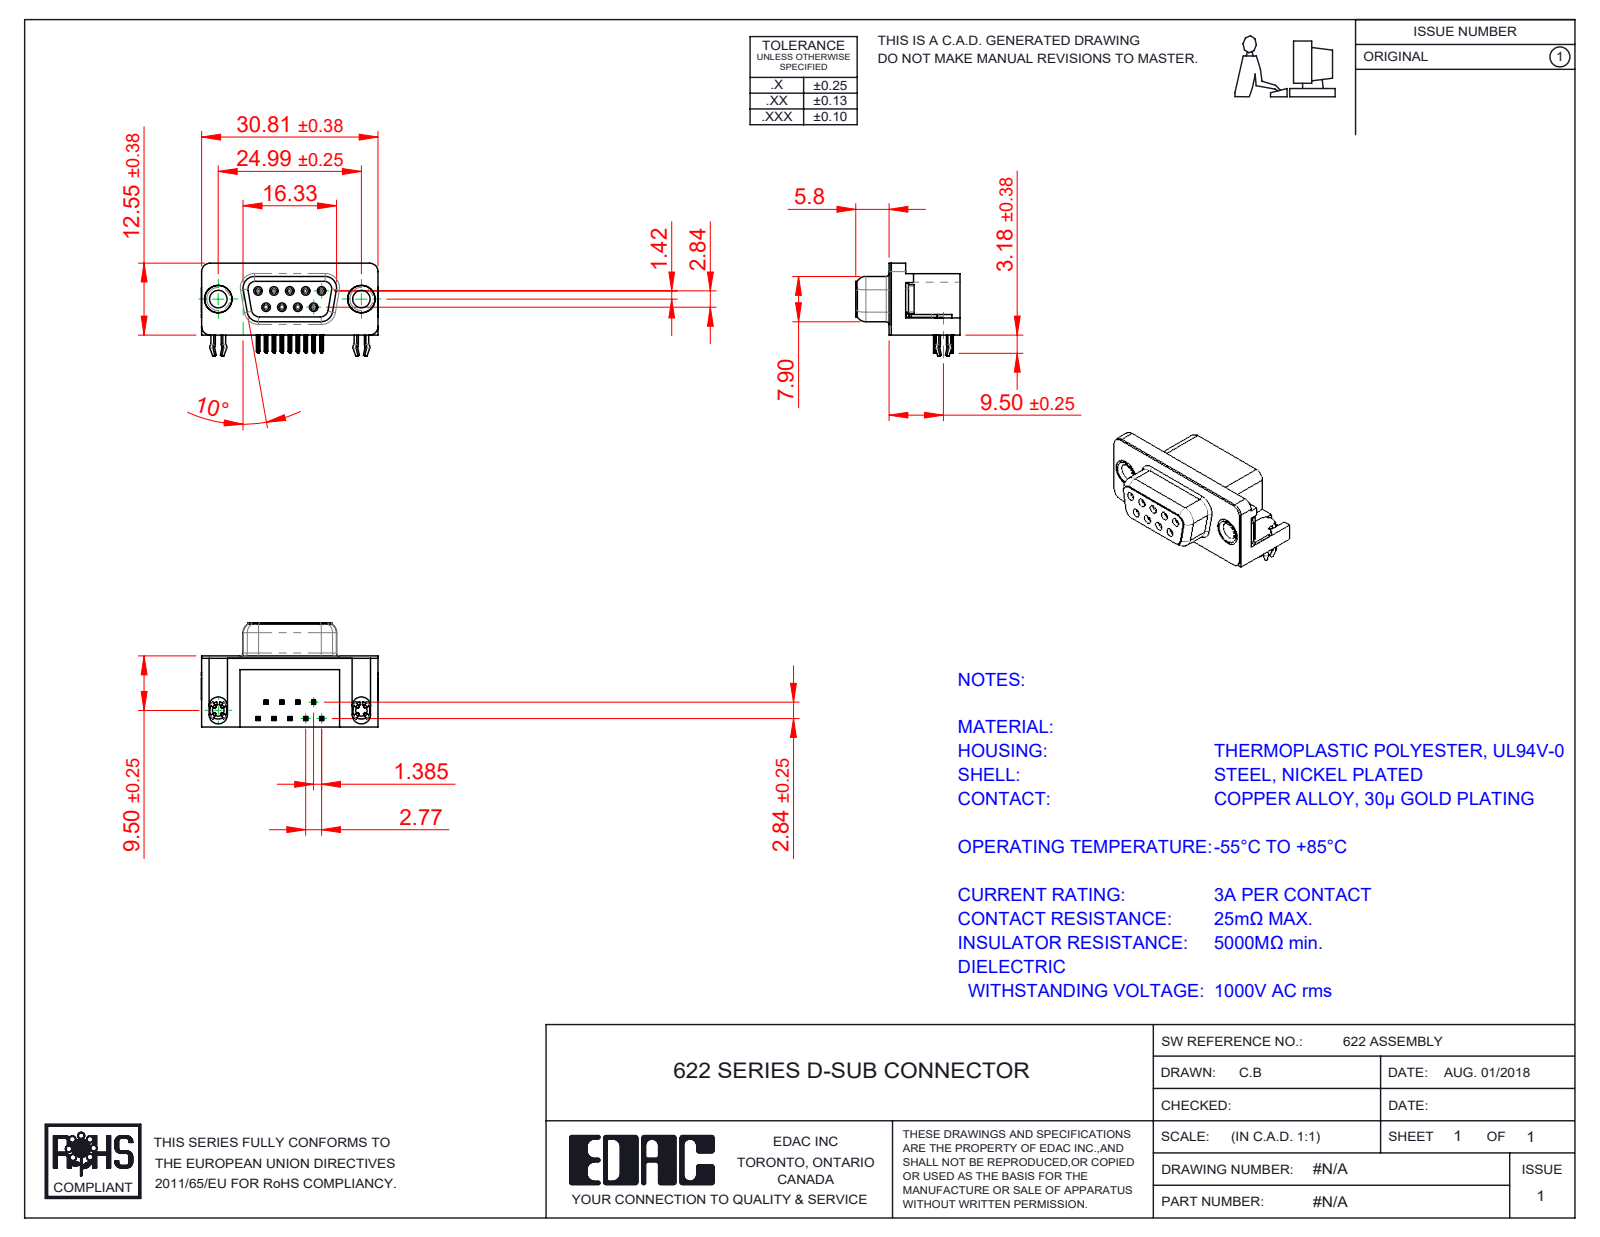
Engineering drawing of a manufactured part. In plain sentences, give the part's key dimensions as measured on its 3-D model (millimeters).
The part is named "622-009-668-051; 622 Thru Hole Rivet; 622 Socket Bottom; 622 Contact Top (+3 more)". Its 3-D file was written by "SolidWorks 2016 (CONFIG_CONTROL_DESIGN)". It is 15 solids with 1562 faces: 684 planar, 410 cylindrical and 468 other. Overall it measures 30.89 by 18.2 by 15.73 millimeters. Its volume is 3 725 cubic millimeters and its surface area 5 129 square millimeters. Round holes: 9 of diameter 0.8, 9 of diameter 0.9, 2 of diameter 2.26, 2 of diameter 3.05, 2 of diameter 4, 2 of diameter 4.8, 2 of diameter 5. Round bosses or shafts: 9 of diameter 1.2, 2 of diameter 4.9, 2 of diameter 4.75, 2 of diameter 3.85, 2 of diameter 3.26. Partial cylindrical surfaces (rounded edges, fillets, slot ends): 72 of radius 0.1, 36 of radius 0.15, 18 of radius 0.35, 18 of radius 1, 9 of radius 0.34, 8 of radius 0.25, 8 of radius 1.35, 8 of radius 1.6. The main face-to-face distances are 0.4, 12, 12.4, 0.35, 2.9, 2.5, 6.2, 10.34, 9.5, 5.8. The hole center spacings are 3.16, 2.77, 5.54, 5.03, 5.04, 8.31, 7.48, 7.49.
